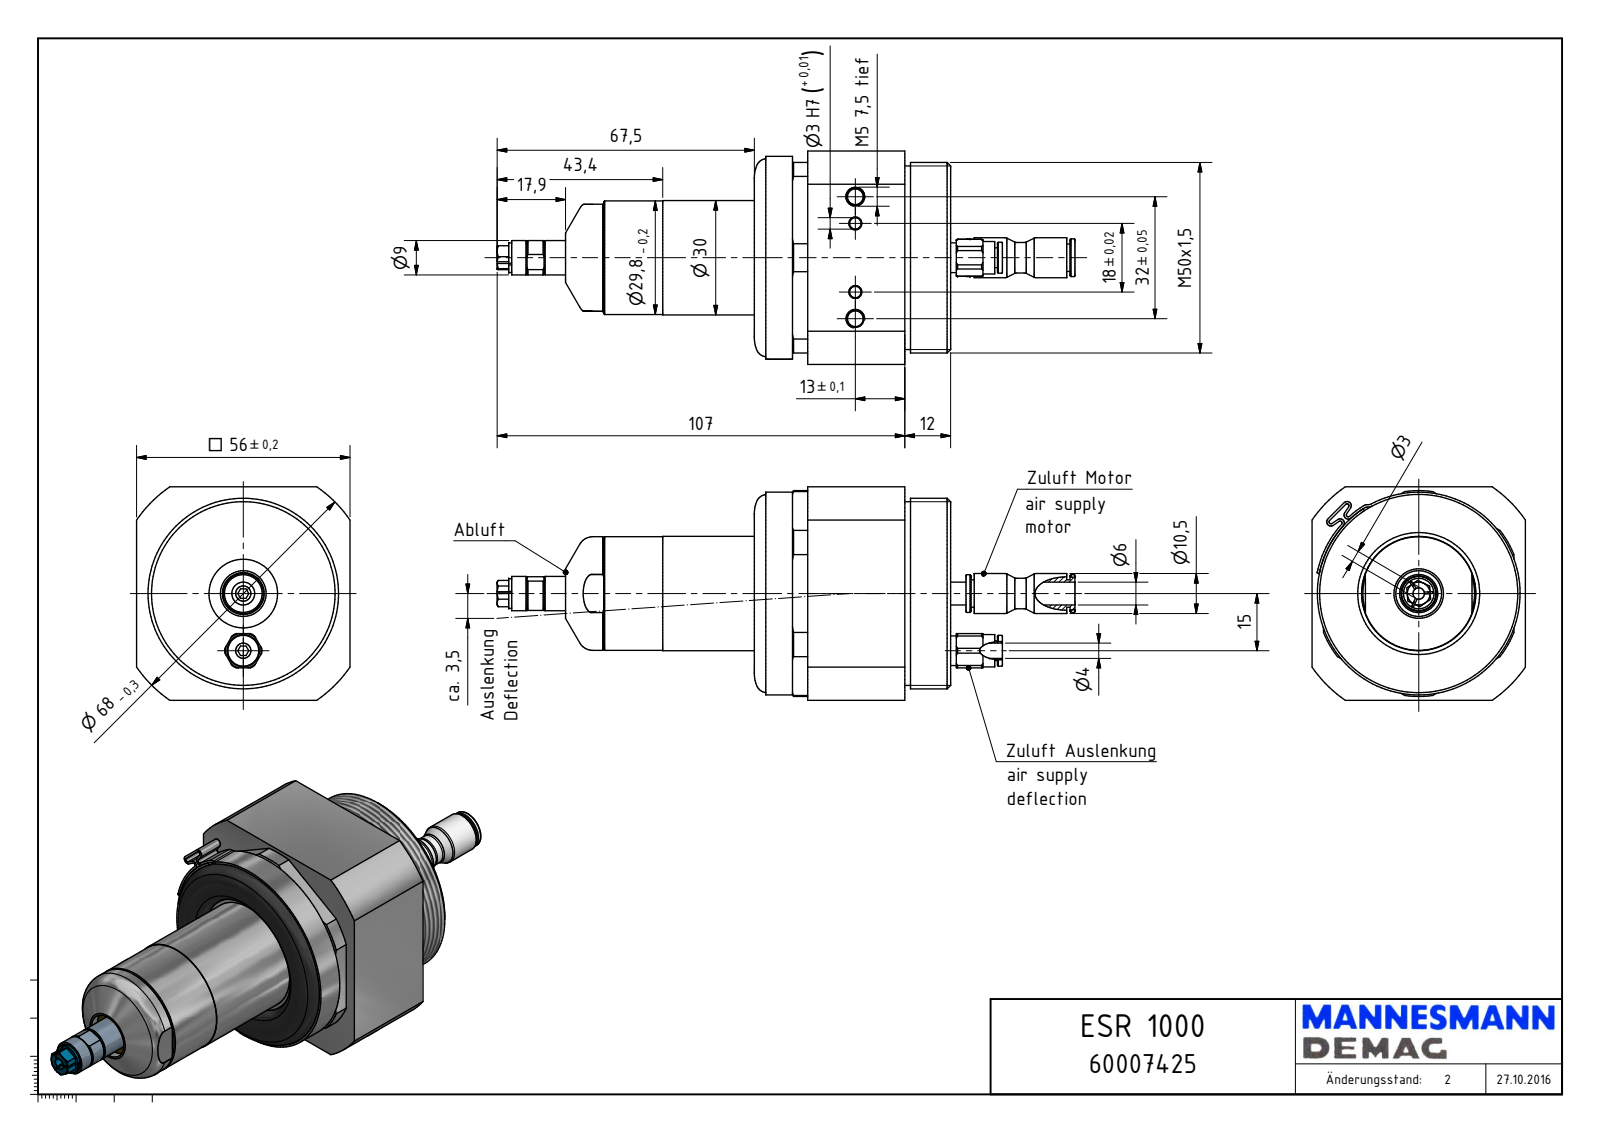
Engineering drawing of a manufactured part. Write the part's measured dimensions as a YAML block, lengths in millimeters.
part_name: "ESR 1000_60007425"
step_written_by: "Autodesk Inventor 2024 (AUTOMOTIVE_DESIGN)"
units: millimeters
bodies: {solids: 1, faces: 321, planar: 140, cylindrical: 99, other: 82}
overall_size: [151.62, 56, 56]
volume: 158568
surface_area: 31803
round_holes:
  - {diameter: 3, count: 3}
  - {diameter: 4.13, count: 3}
  - {diameter: 4, count: 2}
  - {diameter: 3.1, count: 1}
  - {diameter: 4.46, count: 1}
  - {diameter: 6, count: 1}
  - {diameter: 10, count: 1}
  - {diameter: 18, count: 1}
  - {diameter: 46, count: 1}
  - {diameter: 48.38, count: 1}
  - {diameter: 50, count: 1}
  - {diameter: 52, count: 1}
round_bosses_or_shafts:
  - {diameter: 7.8, count: 2}
  - {diameter: 53.2, count: 1}
  - {diameter: 48.18, count: 1}
  - {diameter: 48, count: 1}
  - {diameter: 34, count: 1}
  - {diameter: 32, count: 1}
  - {diameter: 30, count: 1}
  - {diameter: 29.8, count: 1}
partial_cylinders:
  - {radius: 0.5, count: 4}
  - {radius: 1, count: 4}
  - {radius: 1.1, count: 4}
  - {radius: 5, count: 3}
  - {radius: 1.4, count: 2}
  - {radius: 2, count: 2}
  - {radius: 2.5, count: 1}
  - {radius: 4.88, count: 1}
face_to_face_distances: [56, 12, 25.5, 37.5, 10, 47.5, 35.5, 11, 1, 36.5]
hole_center_spacings: [7, 25, 15, 18, 32]
